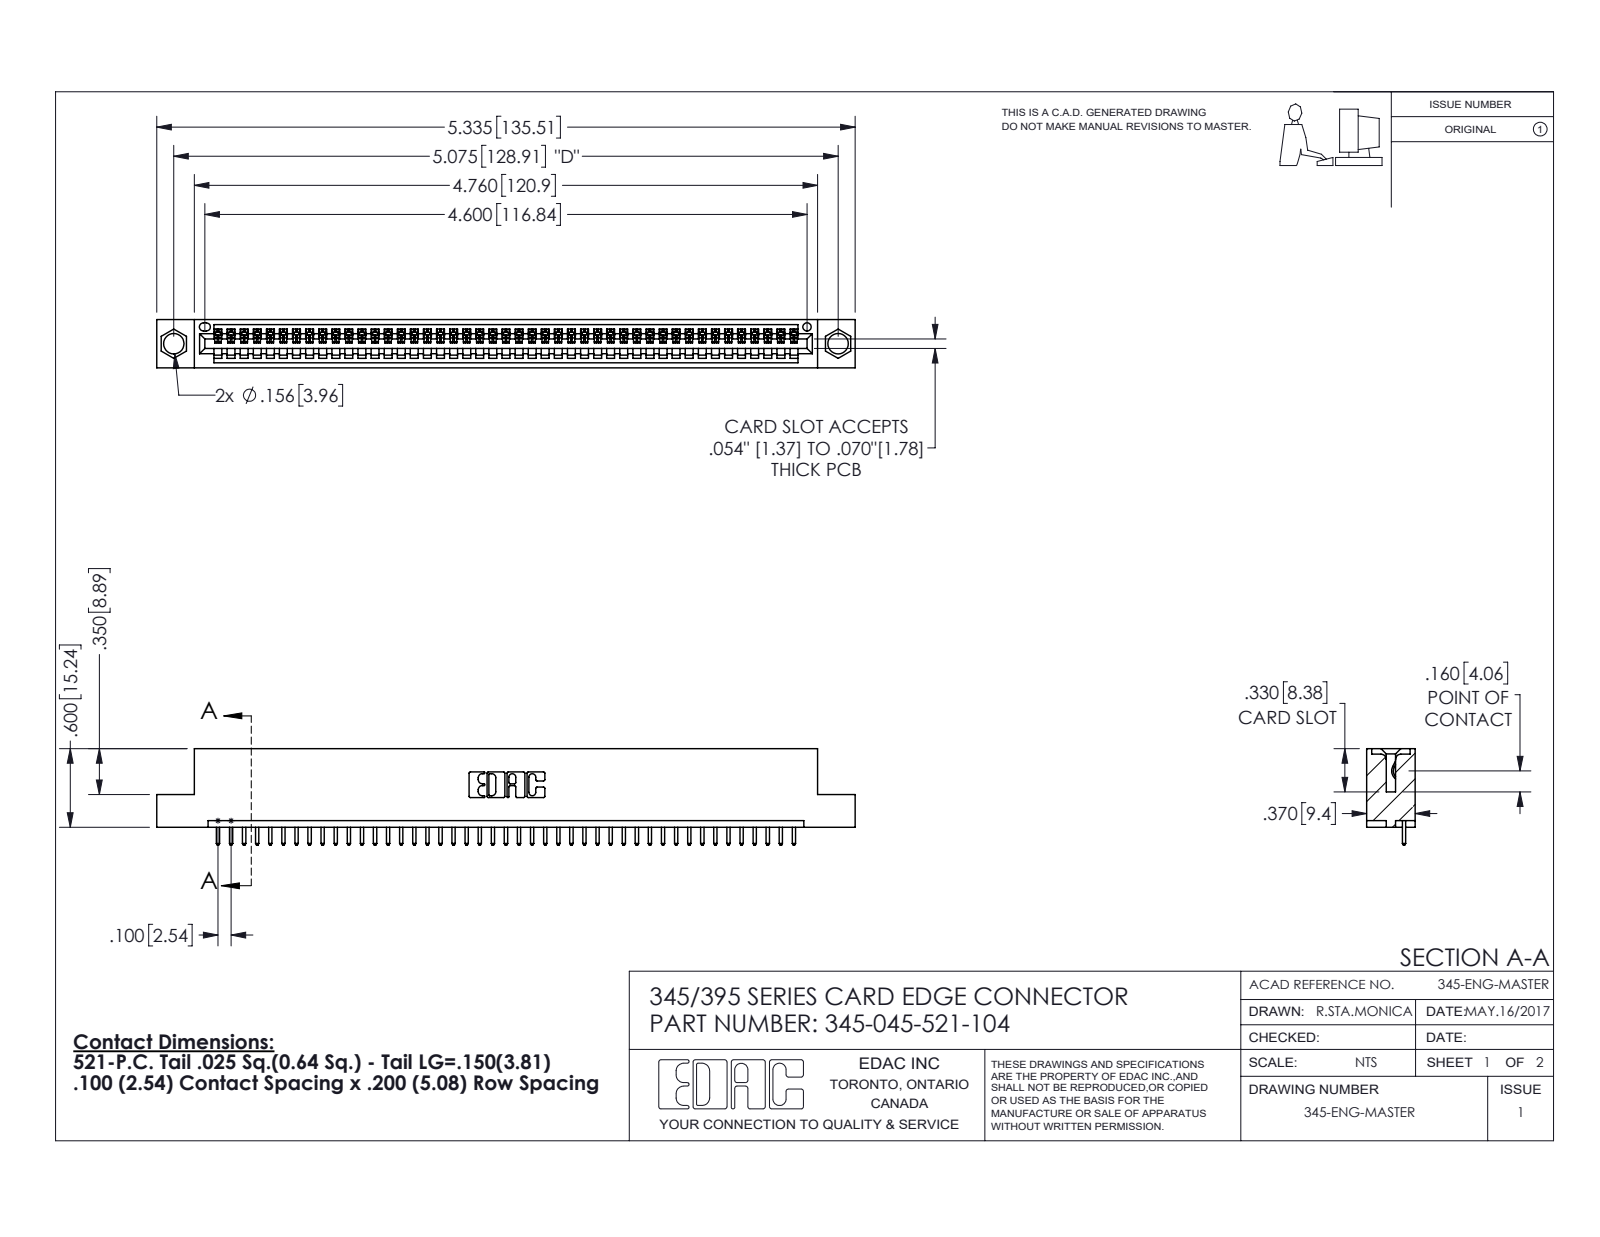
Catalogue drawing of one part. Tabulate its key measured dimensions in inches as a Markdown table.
| quantity | value |
| --- | --- |
| part name | 345-292-001_345-293-121; 345-045-521-104; 345 Part_Flush Mounting Lugs - 0.156 Dia-TH |
| STEP written by | SolidWorks 2016 (CONFIG_CONTROL_DESIGN) |
| units | inches |
| bodies | 46 solids, 2736 faces (1880 planar, 856 cylindrical, 0 other) |
| overall size | 5.335 × 0.737 × 0.37 |
| volume | 0.774 in³ |
| surface area | 25.11 in² |
| round holes (diameter × count) | 0.156 × 2, 0.064 × 1 |
| partial cylindrical surfaces (radius × count) | 0.006 × 90, 0.01 × 90, 0.01 × 22, 0.007 × 6, 0.031 × 6, 0.026 × 3, 0.031 × 2, 0.04 × 2 |
| main face-to-face distances | 0.298, 0.072, 0.37, 0.2, 0.098, 0.272, 0.025, 0.225, 0.149, 0.072 |
| hole center spacings | 0.27, 4.839, 5.075 |
